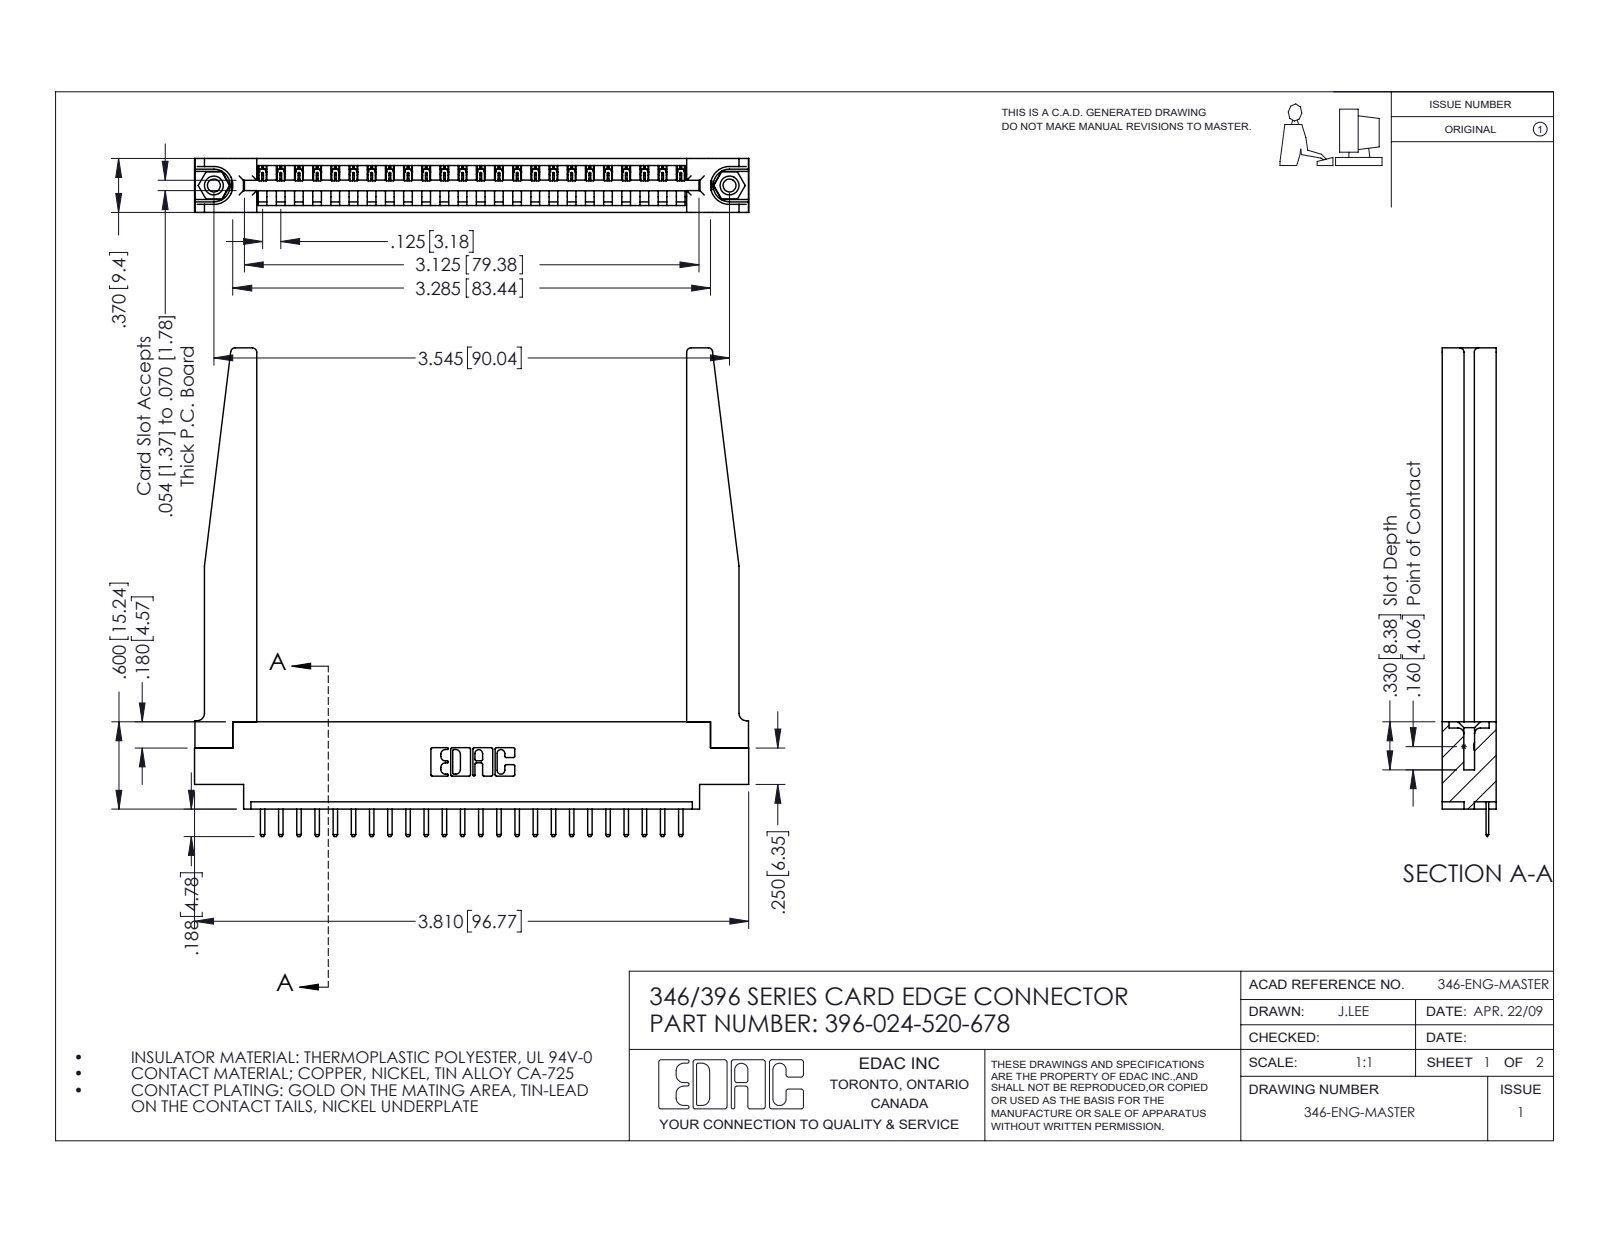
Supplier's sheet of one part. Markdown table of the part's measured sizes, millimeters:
| quantity | value |
| --- | --- |
| part name | 346 Part_0.170 Offset - 0.156 Dia-TH; 345-250-001_345-250-001-102; 346-220-078_345-220-078; 345-292-001_345-293-120 (+1 more) |
| STEP written by | SolidWorks 2016 (CONFIG_CONTROL_DESIGN) |
| units | millimeters |
| bodies | 29 solids, 1848 faces (1230 planar, 566 cylindrical, 52 other) |
| overall size | 96.8 × 85.3 × 9.4 |
| volume | 15 800 mm³ |
| surface area | 17 420 mm² |
| round holes (diameter × count) | 2.3 × 2, 3.2 × 2, 4 × 2, 1.6 × 1 |
| round bosses / shafts (diameter × count) | 3.9 × 2 |
| partial cylindrical surfaces (radius × count) | 0.3 × 50, 0.2 × 48, 0.3 × 22, 0.8 × 8, 0.2 × 6, 0.8 × 6, 0.7 × 3, 0.8 × 2 |
| main face-to-face distances | 9.4, 1.2, 8.2, 3.8, 1.8, 3.8, 6.4, 5.6, 2.5, 4.4 |
| hole center spacings | 6.2, 84.8, 90 |
